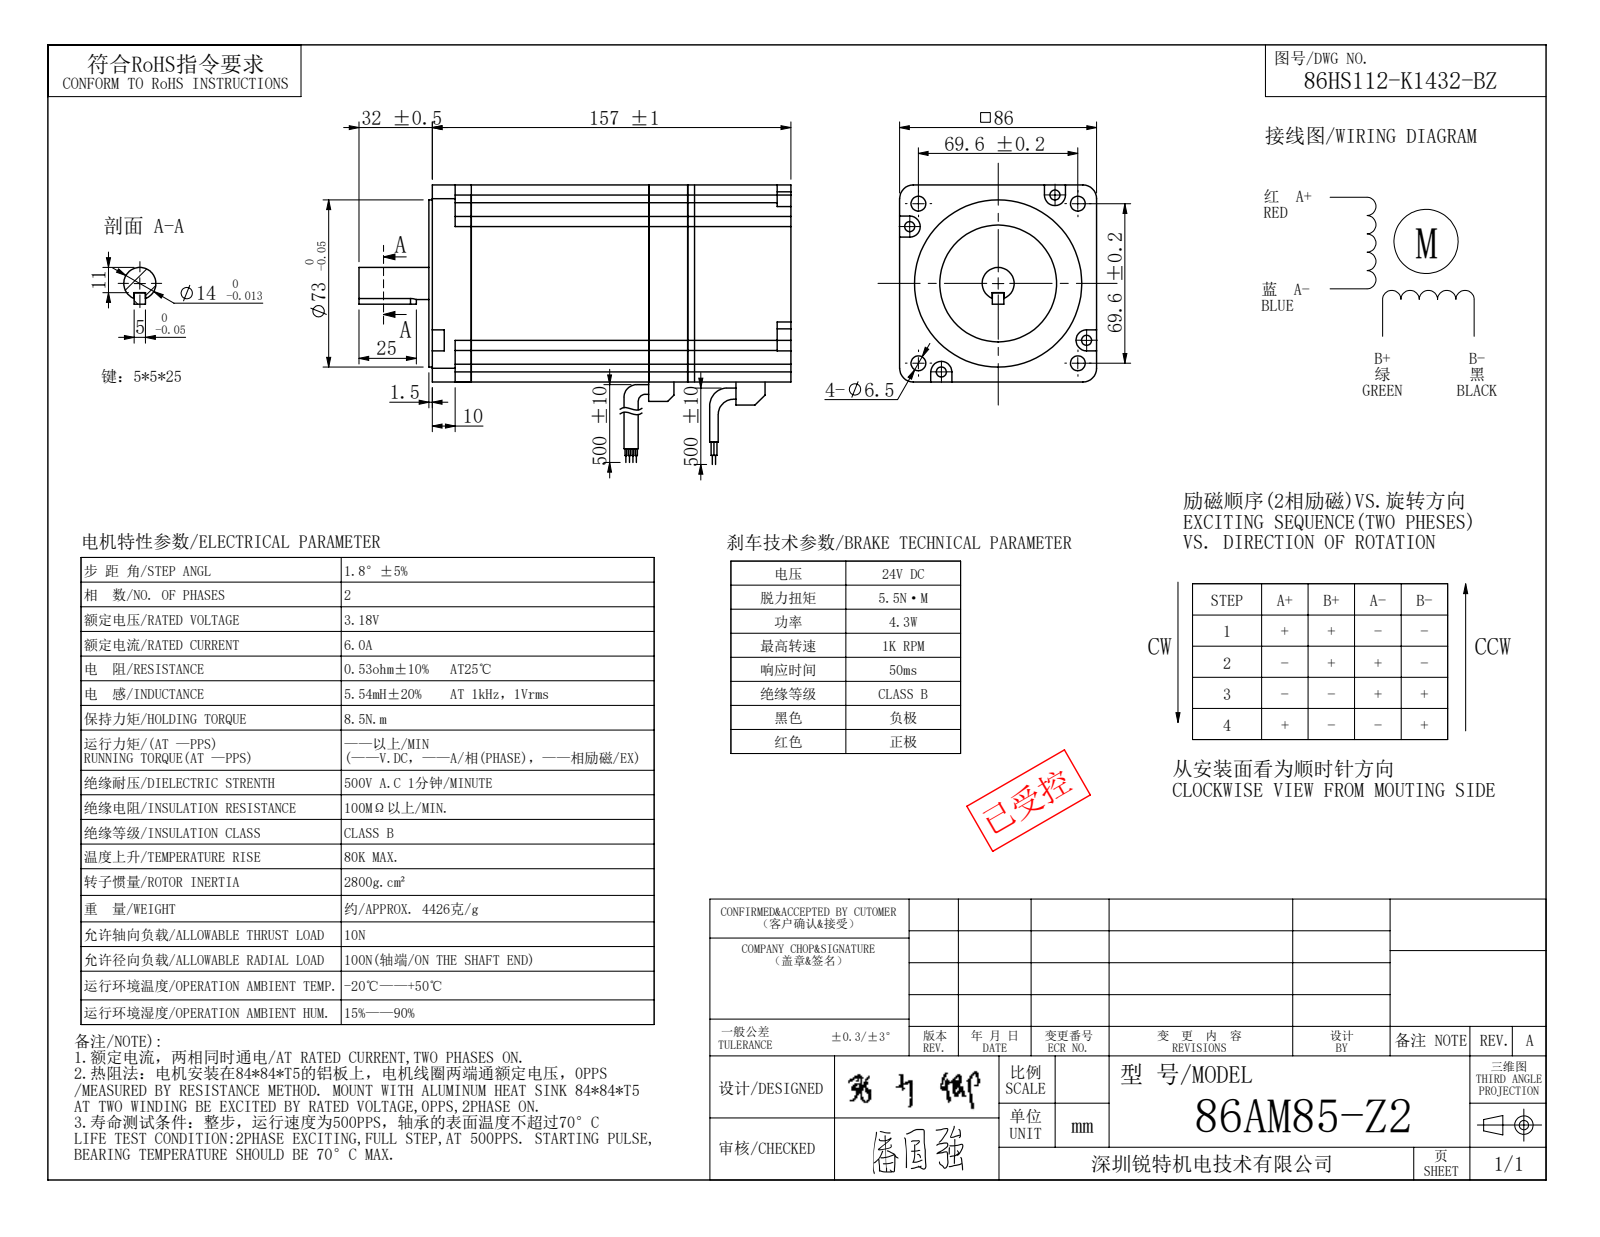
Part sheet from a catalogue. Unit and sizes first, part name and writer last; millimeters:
Units: millimetres
Overall size (bounding box): 185.5 × 86 × 86
Round holes (diameter × count): ⌀4.4 ×8, ⌀4 ×4, ⌀6.5 ×4, ⌀40 ×1, ⌀51 ×1, ⌀80.8 ×1
Round bosses / shafts (diameter × count): ⌀73 ×1, ⌀52 ×1, ⌀14 ×1
Partial cylindrical surfaces — rounded edges, fillets, slot ends (radius × count): R4.4 ×9, R3 ×4, R4.6 ×4, R5 ×4, R6 ×4, R6.05 ×4, R2.5 ×1, R4.41 ×1
Main face-to-face distances: 86, 17, 94.5, 42, 59, 153.5, 111.5, 13.8, 143.5, 72.2
Hole centre spacings: 10.7, 45.88, 59.72, 64.88, 74.08, 94.55, 19.52, 49.21
Volume: 597 278 mm³ · Surface area: 130 399 mm²
Bodies: 5 solids, 235 faces (107 planar, 128 cylindrical, 0 other)
STEP written by: SolidWorks 2014 (AUTOMOTIVE_DESIGN)
